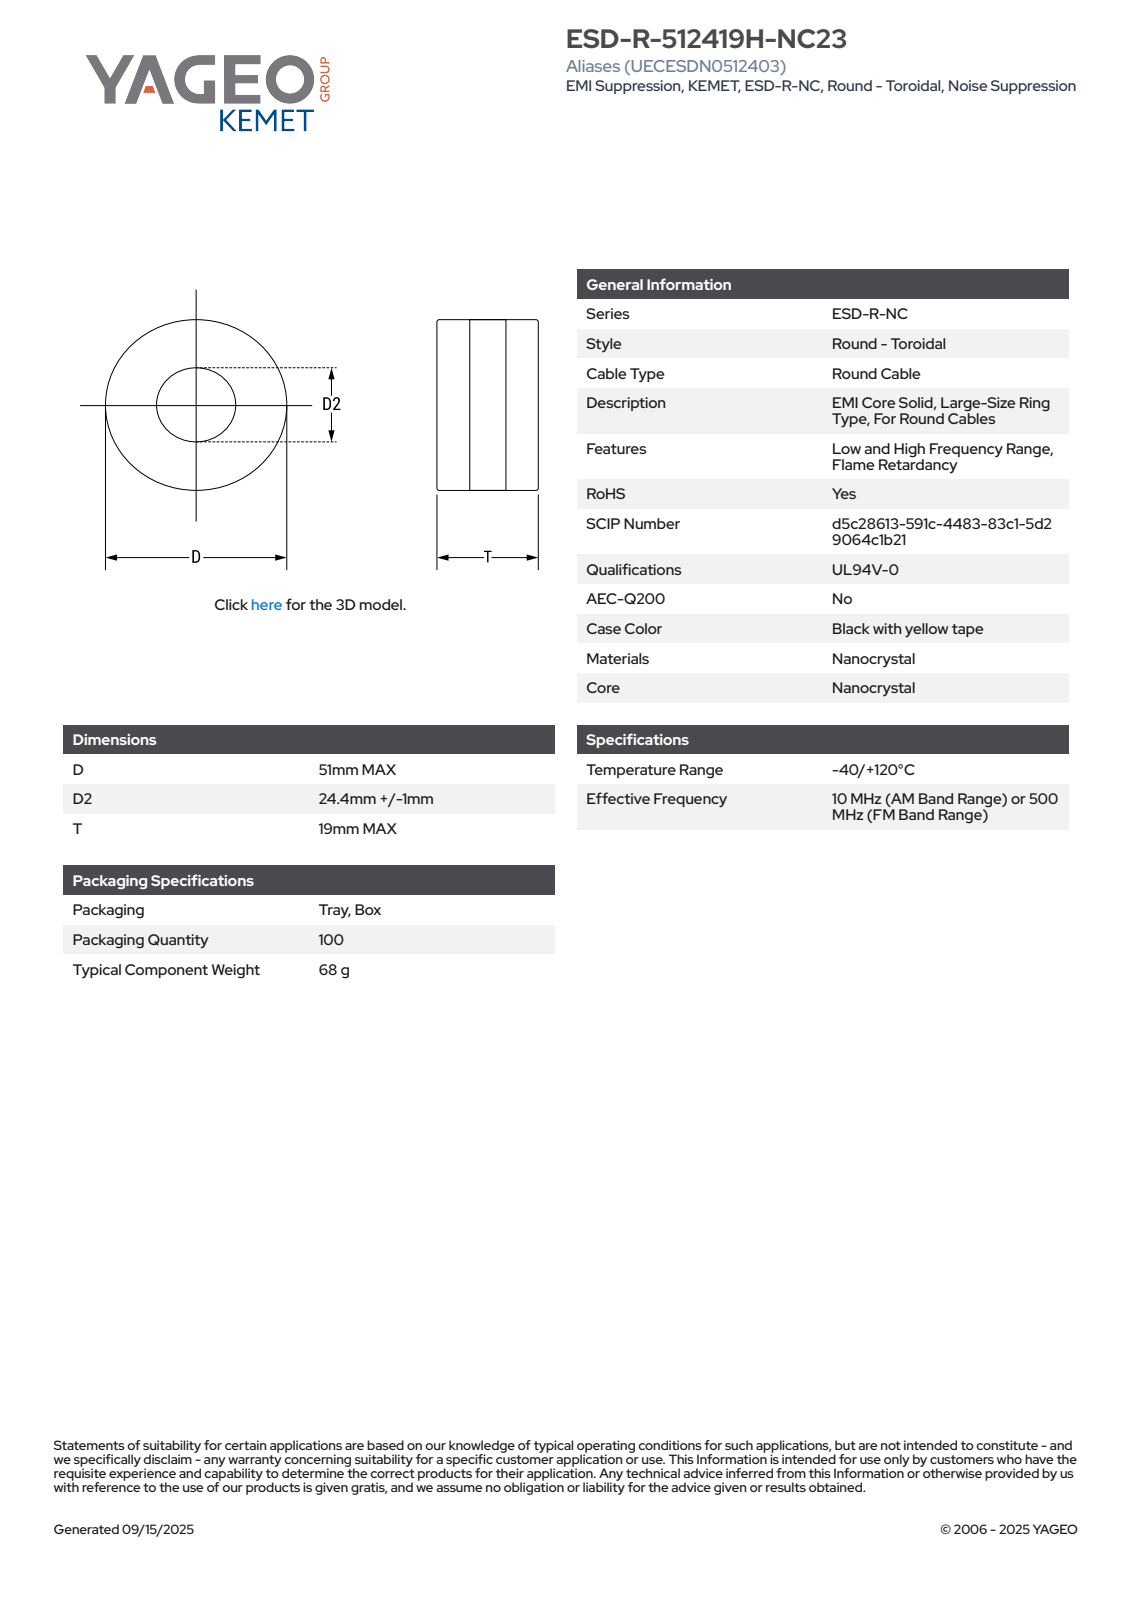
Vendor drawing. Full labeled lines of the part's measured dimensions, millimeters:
Part name (STEP PRODUCT): EC_ESDRNC23_D51D225.4T19
STEP written by: SolidWorks 2014 (AUTOMOTIVE_DESIGN)
Units: millimetres
Bodies: 1 solid, 74 faces (26 planar, 9 cylindrical, 39 other)
Overall size (bounding box): 51.03 × 51.02 × 19
Volume: 29 148 mm³ · Surface area: 7 489 mm²
Round holes (diameter × count): ⌀25.4 ×1
Round bosses / shafts (diameter × count): ⌀51.02 ×1, ⌀51 ×1
Partial cylindrical surfaces — rounded edges, fillets, slot ends (radius × count): R25.52 ×1
Main face-to-face distances: 19, 6.37, 18.25, 11.88, 12.63, 0.75, 8.04, 1.67, 10.21, 10.96
